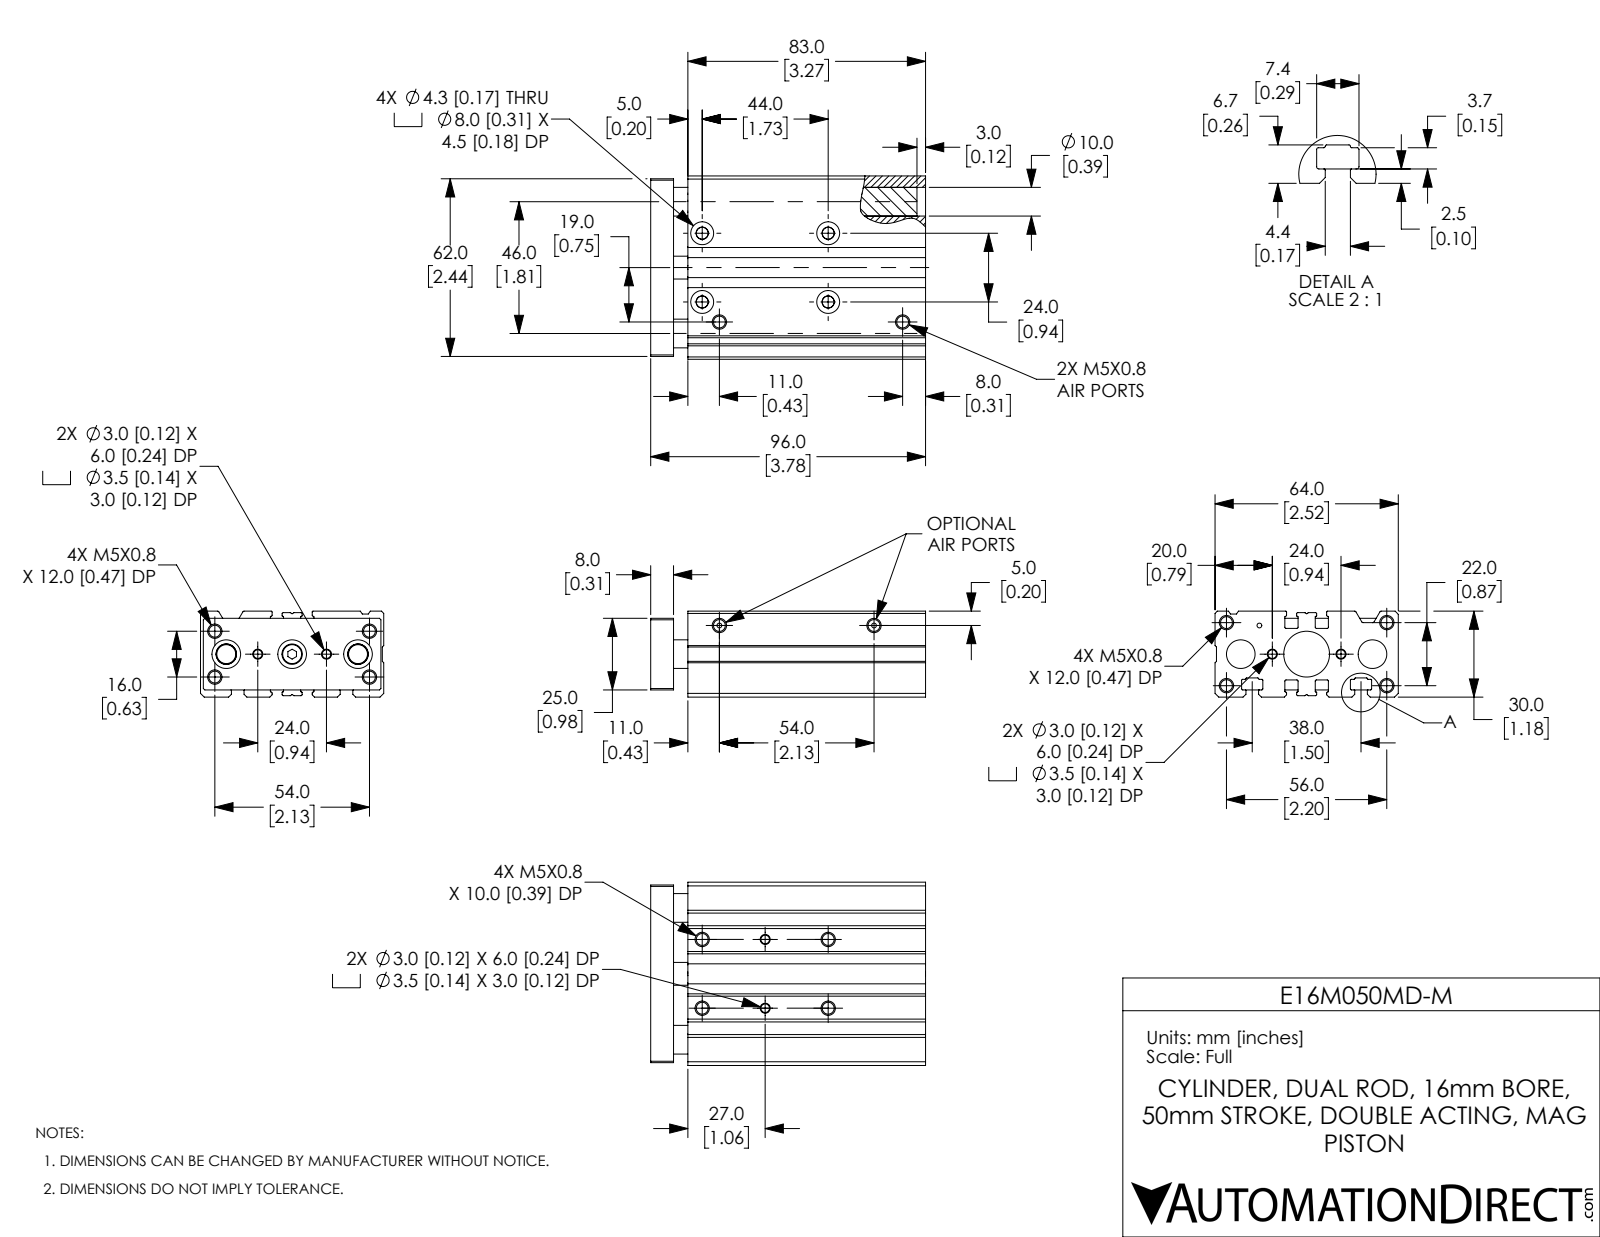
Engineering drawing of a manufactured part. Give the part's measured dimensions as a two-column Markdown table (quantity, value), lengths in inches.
| quantity | value |
| --- | --- |
| part name | E16M050MD-M_BODY; E16M050MD-M_ENDPLATE; E16M050MD-M |
| STEP written by | SolidWorks 2019 (CONFIG_CONTROL_DESIGN) |
| units | inches |
| bodies | 5 solids, 411 faces (133 planar, 192 cylindrical, 86 other) |
| overall size | 3.78 × 2.52 × 1.181 |
| volume | 8.607 in³ |
| surface area | 82.46 in² |
| round holes (diameter × count) | 0.163 × 16, 0.118 × 4, 0.138 × 4, 0.169 × 4, 0.315 × 4, 0.066 × 3, 0.197 × 3, 0.394 × 3, 0.28 × 2, 0.394 × 1, 0.63 × 1, 0.63 × 1 |
| round bosses / shafts (diameter × count) | 0.315 × 1, 0.28 × 1 |
| partial cylindrical surfaces (radius × count) | 0.008 × 22, 0.016 × 20, 0.01 × 8, 0.012 × 6, 0.02 × 4 |
| main face-to-face distances | 1.181, 0.02, 0.236, 2.52, 0.138, 1.142, 1.083, 0.945, 0.157, 0.961 |
| hole center spacings | 0.866, 0.124, 0.352, 0.476, 0.669, 0.749, 0.765, 0.945 |
